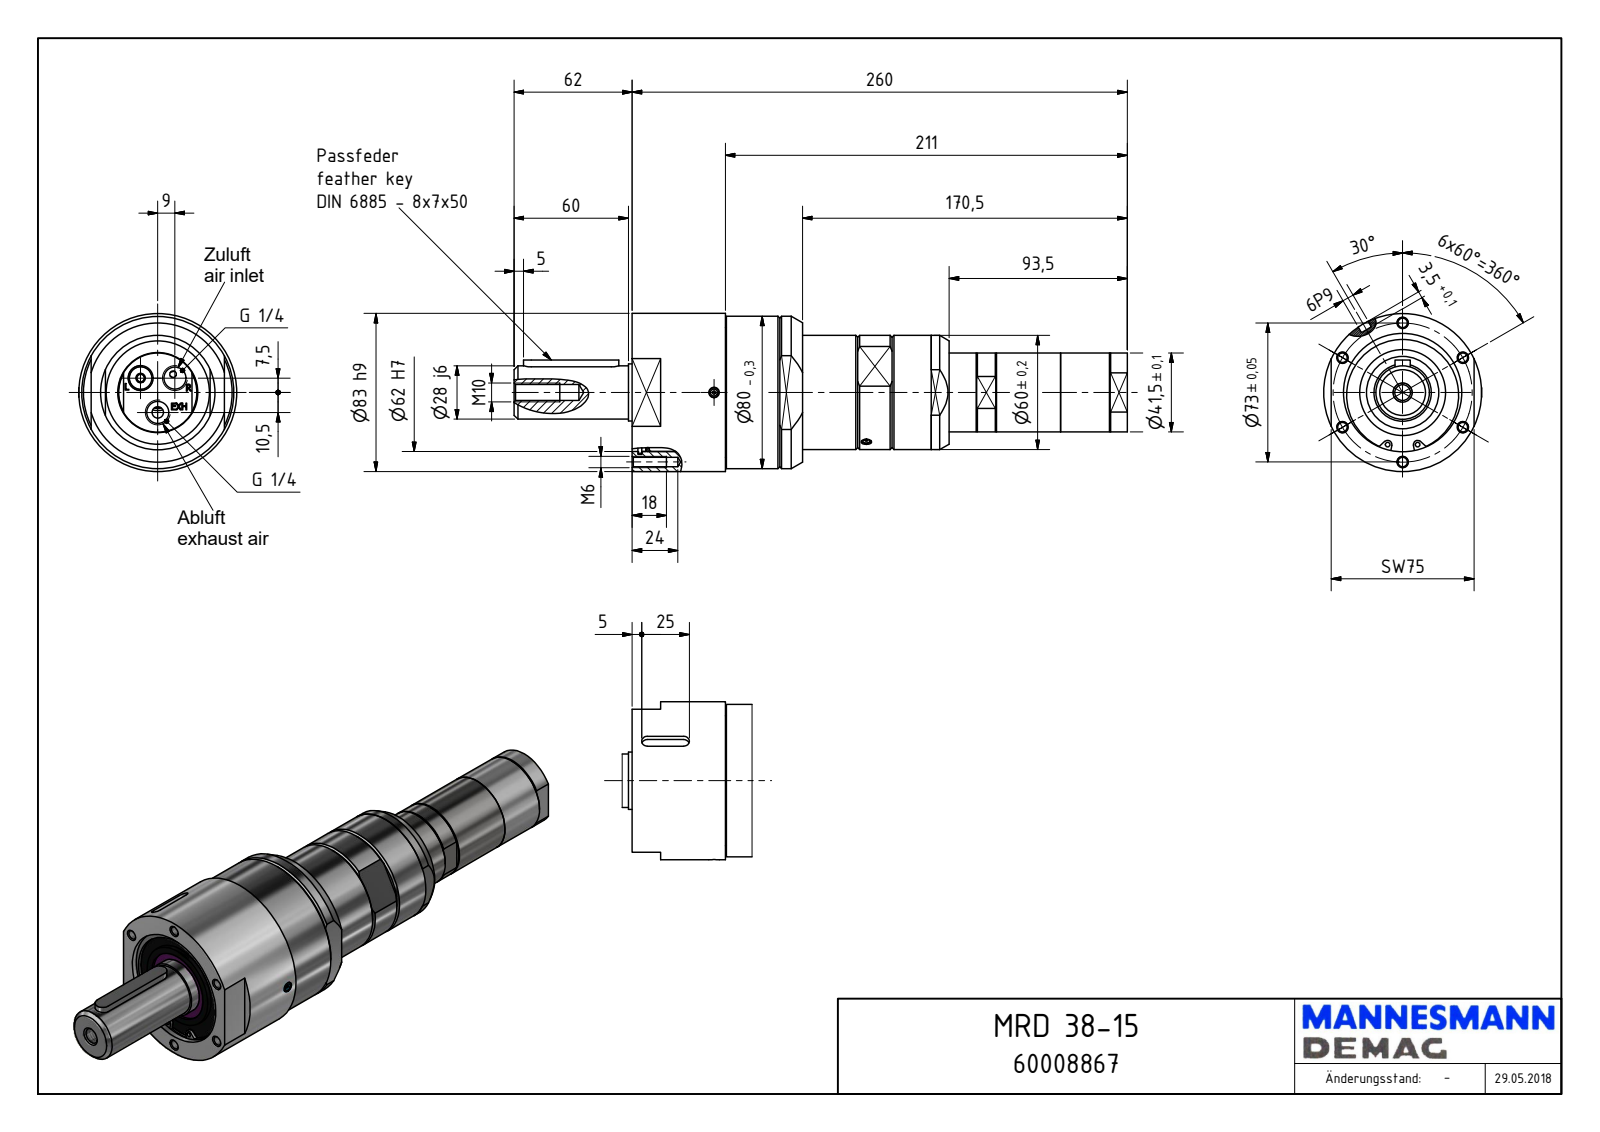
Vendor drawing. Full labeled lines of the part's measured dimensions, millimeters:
Part name (STEP PRODUCT): MRD 38-15_60008867
STEP written by: Autodesk Inventor 2018 (AUTOMOTIVE_DESIGN)
Units: millimetres
Bodies: 1 solid, 595 faces (250 planar, 274 cylindrical, 71 other)
Overall size (bounding box): 322 × 83 × 83
Volume: 818 346 mm³ · Surface area: 84 627 mm²
Round holes (diameter × count): ⌀4.92 ×6, ⌀4 ×3, ⌀11.45 ×3, ⌀1.55 ×2, ⌀5.5 ×2, ⌀8.38 ×1, ⌀38 ×1, ⌀40 ×1, ⌀42 ×1, ⌀50.38 ×1, ⌀62 ×1, ⌀65 ×1
Round bosses / shafts (diameter × count): ⌀5 ×2, ⌀3.6 ×2, ⌀3.3 ×2, ⌀83 ×1, ⌀80 ×1, ⌀68.18 ×1, ⌀67 ×1, ⌀60 ×1
Partial cylindrical surfaces — rounded edges, fillets, slot ends (radius × count): R3.5 ×94, R3 ×2, R4 ×2, R24.16 ×1, R24.96 ×1, R33.01 ×1
Main face-to-face distances: 49, 2.5, 0.5, 44, 5, 89.5, 84.5, 40.5, 49.5, 44.5
Hole centre spacings: 36.5, 63.22, 73, 11.72, 20.12, 25.04, 30.36, 32.55
